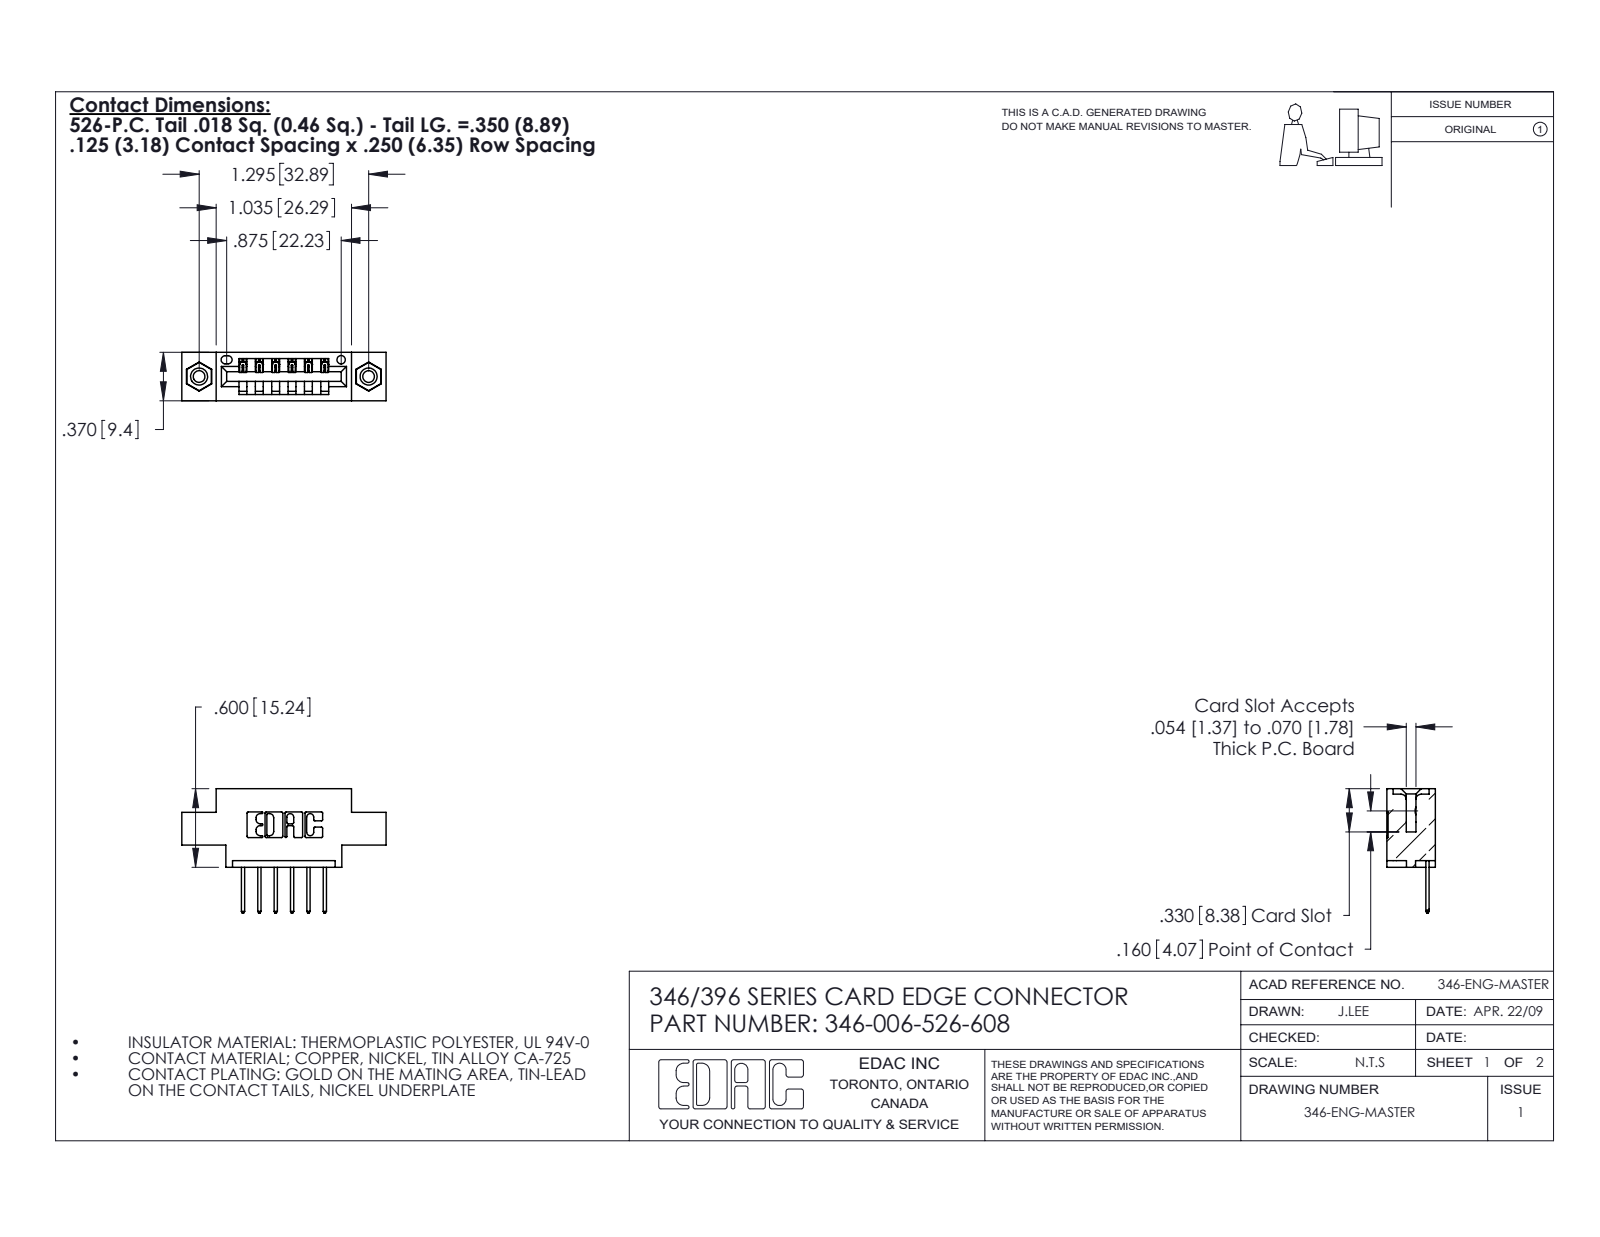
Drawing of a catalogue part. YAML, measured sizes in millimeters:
part_name: "345-250-001_345-250-003-102; 345-292-001_345-293-126; 346-006-526-608; 346 Part_0.170 Offset - 0.156 Dia-TI"
step_written_by: "SolidWorks 2020 (CONFIG_CONTROL_DESIGN)"
units: millimeters
bodies: {solids: 9, faces: 534, planar: 352, cylindrical: 166, other: 16}
overall_size: [39.6, 24.1, 9.4]
volume: 3380
surface_area: 4011
round_holes:
  - {diameter: 2.3, count: 2}
  - {diameter: 3.2, count: 2}
  - {diameter: 4, count: 2}
  - {diameter: 1.6, count: 1}
round_bosses_or_shafts:
  - {diameter: 3.9, count: 2}
partial_cylinders:
  - {radius: 0.3, count: 22}
  - {radius: 0.2, count: 12}
  - {radius: 0.3, count: 12}
  - {radius: 0.2, count: 6}
  - {radius: 0.8, count: 6}
  - {radius: 0.7, count: 3}
  - {radius: 0.8, count: 2}
  - {radius: 1, count: 2}
face_to_face_distances: [6.4, 9.4, 1.2, 8.2, 5.6, 3.8, 2.5, 4.4, 1.8, 7.6]
hole_center_spacings: [6.2, 27.7, 32.9]
